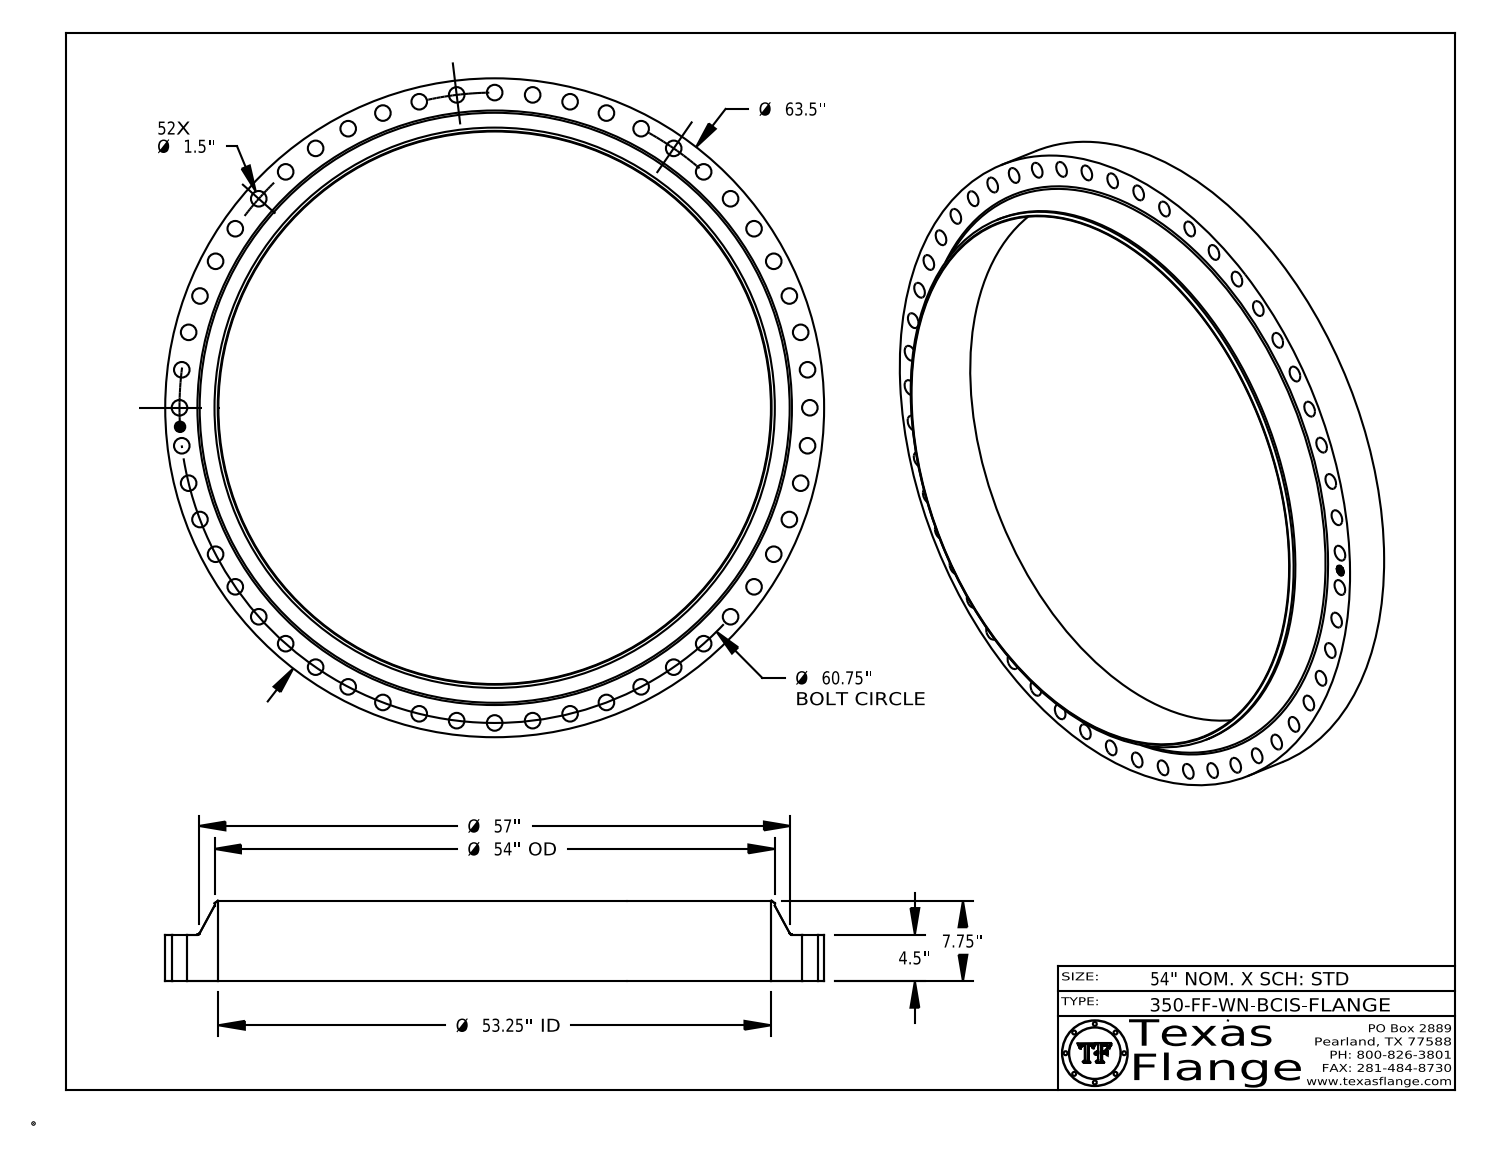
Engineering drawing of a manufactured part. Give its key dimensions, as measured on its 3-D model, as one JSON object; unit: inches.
{"part_name": "350-FF-WN, BCIS", "step_written_by": "CATIA V5 STEP AP214 (AUTOMOTIVE_DESIGN)", "units": "inches", "bodies": {"solids": 1, "faces": 504, "planar": 368, "cylindrical": 130, "other": 6}, "overall_size": [63.5, 63.5, 7.75], "volume_in3": 4375, "surface_area_in2": 5330, "round_holes": [[1.5, 52], [1, 1], [53.25, 1]], "round_bosses_or_shafts": [[0.061, 8], [63.5, 1], [54, 1], [0.788, 1]], "face_to_face_distances": [4.5, 7.75, 3.25, 4.485, 0.015, 3.265, 0.298, 0.293, 0.019, 0.054], "hole_center_spacings": [30.375, 3.668, 59.755, 60.307, 60.639, 7.323, 56.802, 10.951]}
